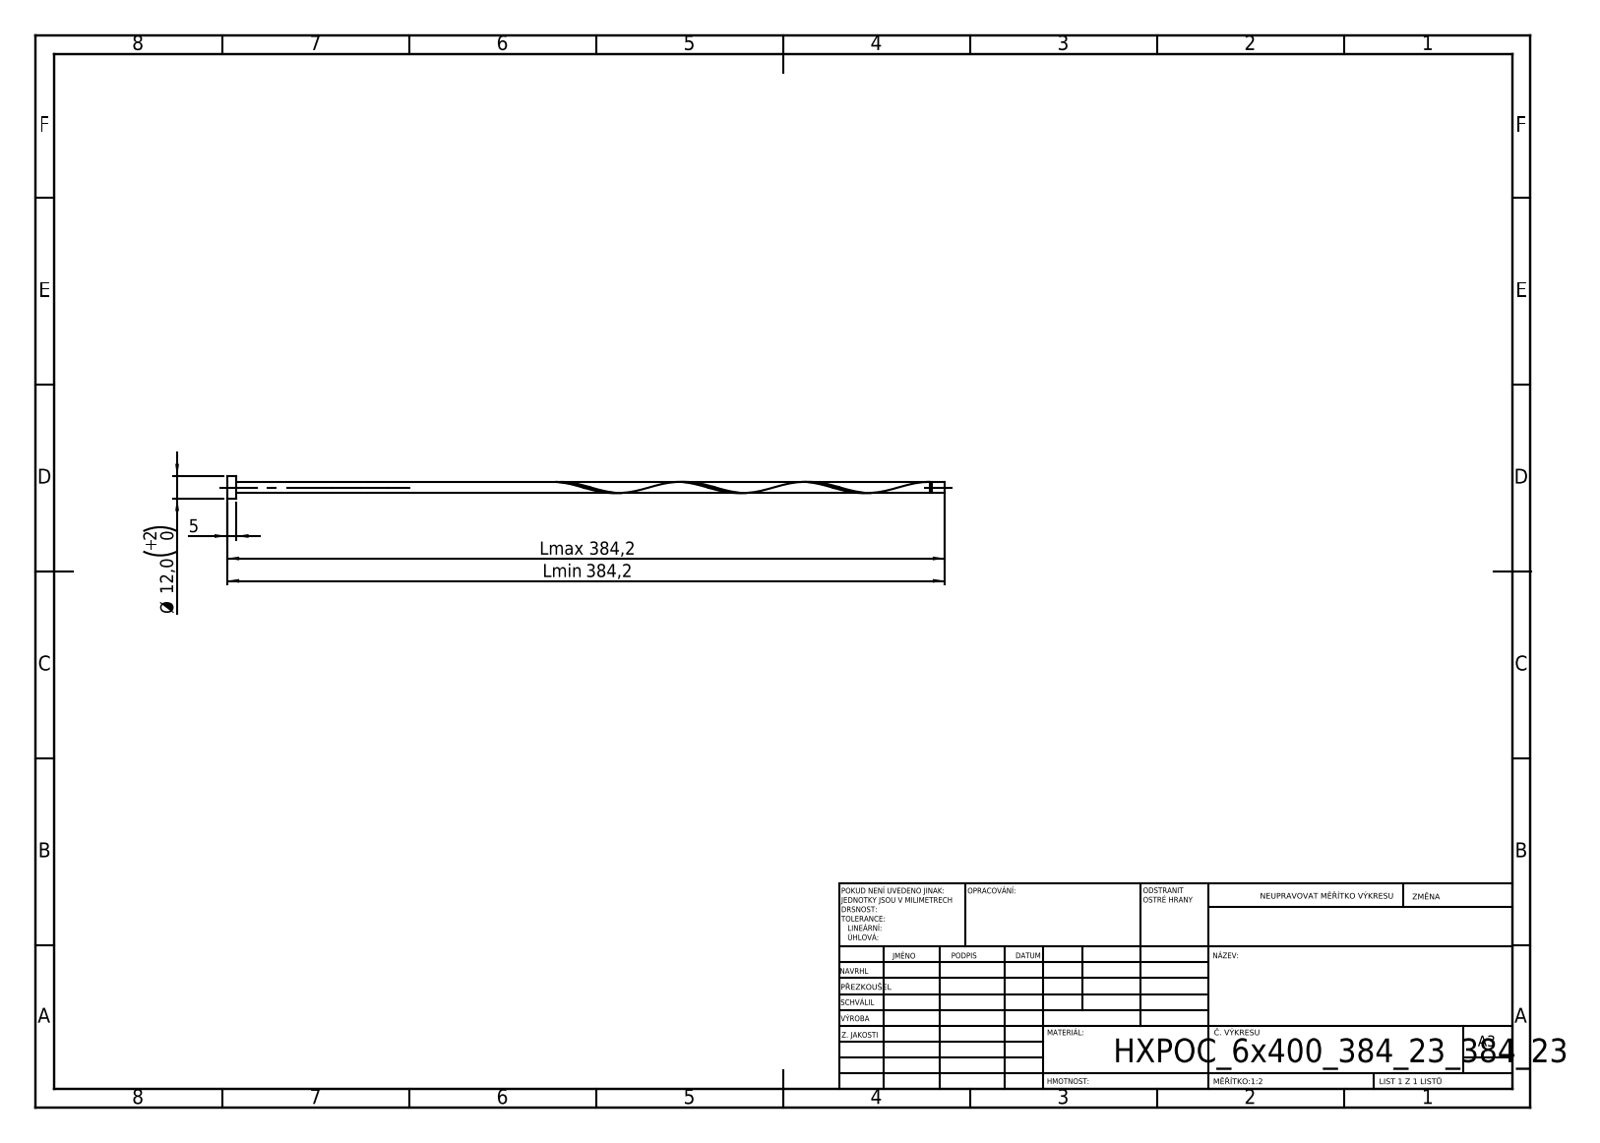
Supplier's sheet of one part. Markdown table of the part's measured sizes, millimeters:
| quantity | value |
| --- | --- |
| STEP written by | SolidWorks 2019 (CONFIG_CONTROL_DESIGN) |
| units | millimeters |
| bodies | 1 solid, 16 faces (6 planar, 9 cylindrical, 1 other) |
| overall size | 384.23 × 12 × 12 |
| volume | 13 682 mm³ |
| surface area | 10 212 mm² |
| round bosses / shafts (diameter × count) | 12 × 1, 6 × 1, 4.8 × 1 |
| main face-to-face distances | 5, 384.23, 379.23, 377.1, 372.1, 7.13, 375.9, 370.9, 1.2, 8.33 |
